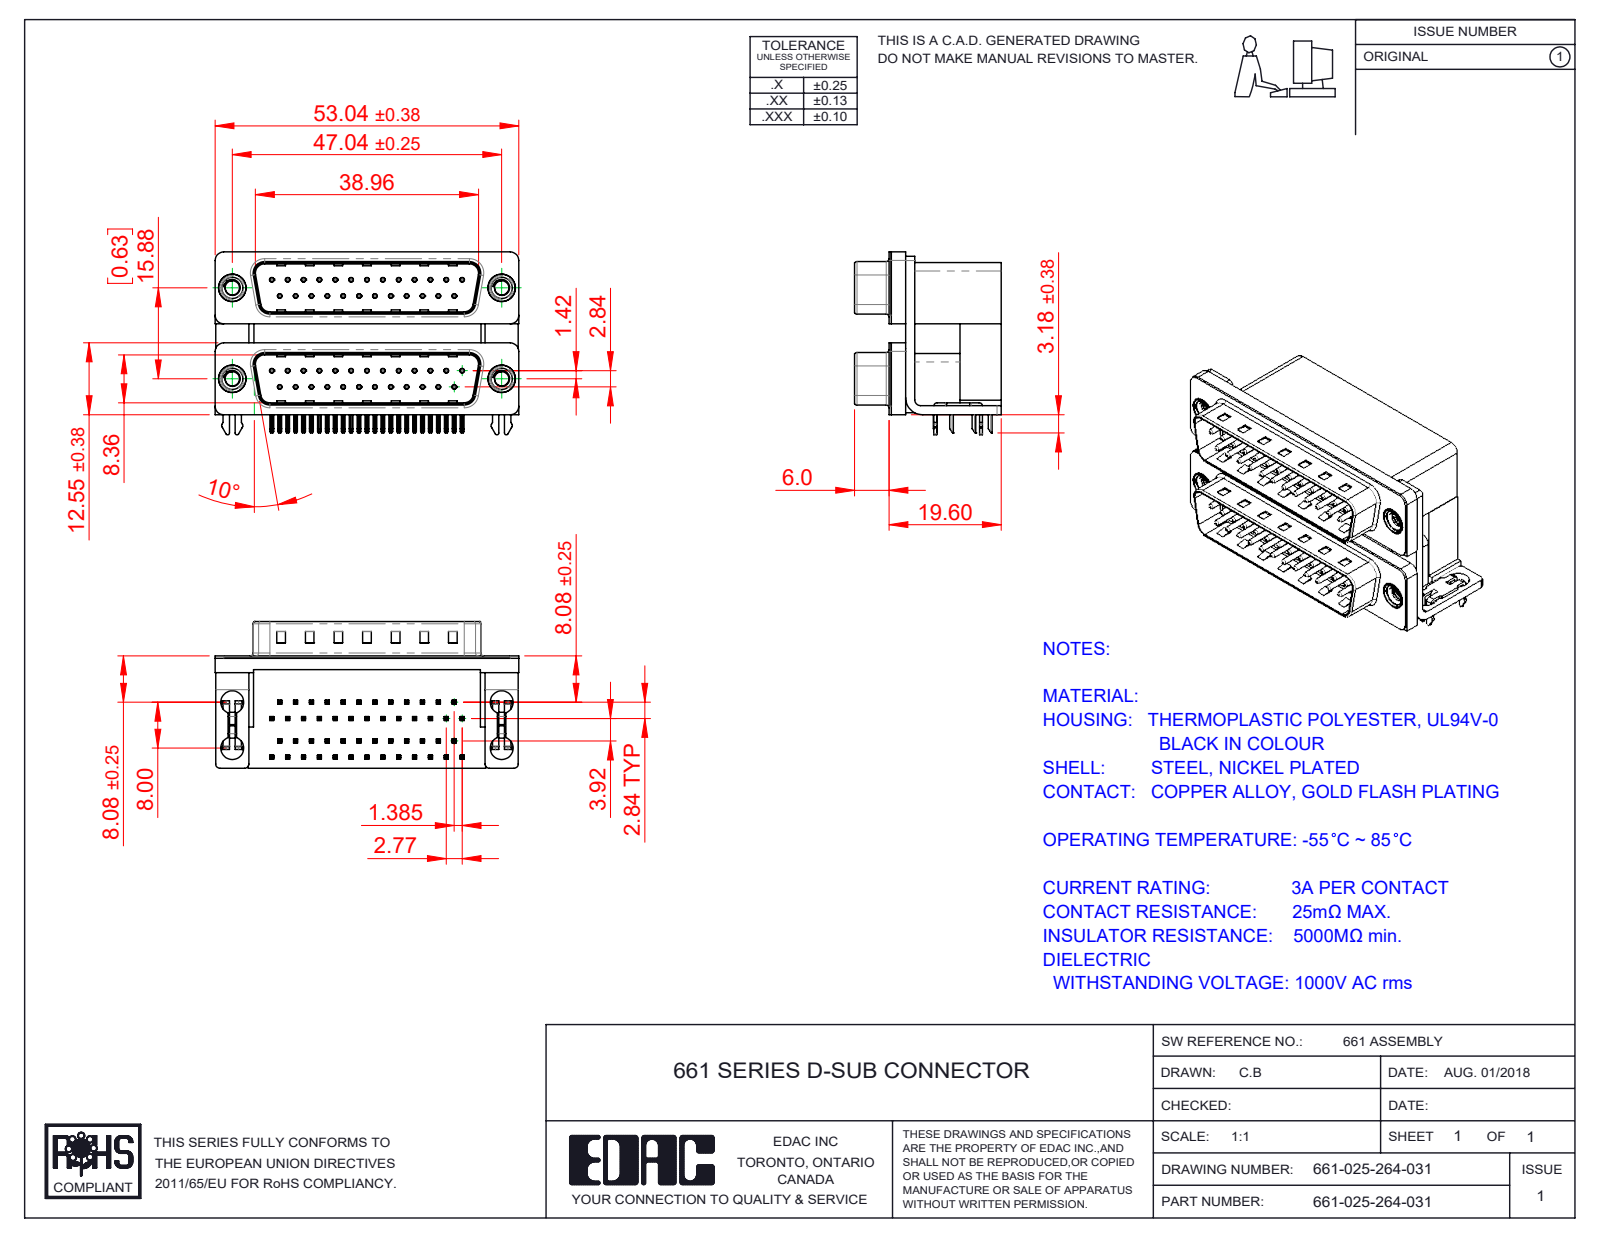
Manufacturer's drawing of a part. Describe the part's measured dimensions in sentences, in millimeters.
The part is named "661 Housing Spacer_25 Contacts L; 661 Shell_25 Contacts; 661-025-264-031; 661 Housing Lower_25 Contacts (+8 more)". Its 3-D file was written by "SolidWorks 2020 (CONFIG_CONTROL_DESIGN)". It is 63 solids with 4770 faces: 3040 planar, 1340 cylindrical and 390 other. Overall it measures 53.04 by 31.93 by 25.6 millimeters. Its volume is 20 267 cubic millimeters and its surface area 21 493 square millimeters. Round holes: 50 of diameter 0.35, 50 of diameter 0.8, 8 of diameter 4, 4 of diameter 2.5, 4 of diameter 3.5, 4 of diameter 4.8, 4 of diameter 5. Round bosses or shafts: 50 of diameter 0.75, 4 of diameter 4.9, 4 of diameter 4.75, 4 of diameter 3.9. Partial cylindrical surfaces (rounded edges, fillets, slot ends): 210 of radius 0.25, 100 of radius 0.12, 20 of radius 0.5, 13 of radius 1.5, 10 of radius 0.75, 8 of radius 0.9, 8 of radius 1.6, 8 of radius 2. The main face-to-face distances are 0.4, 19.2, 7.2, 12, 10.7, 15.87, 16.7, 9.5, 2.5, 15.53. The hole center spacings are 3.16, 2.77, 5.54, 8.31, 11.08, 13.85, 16.62, 5.03.
